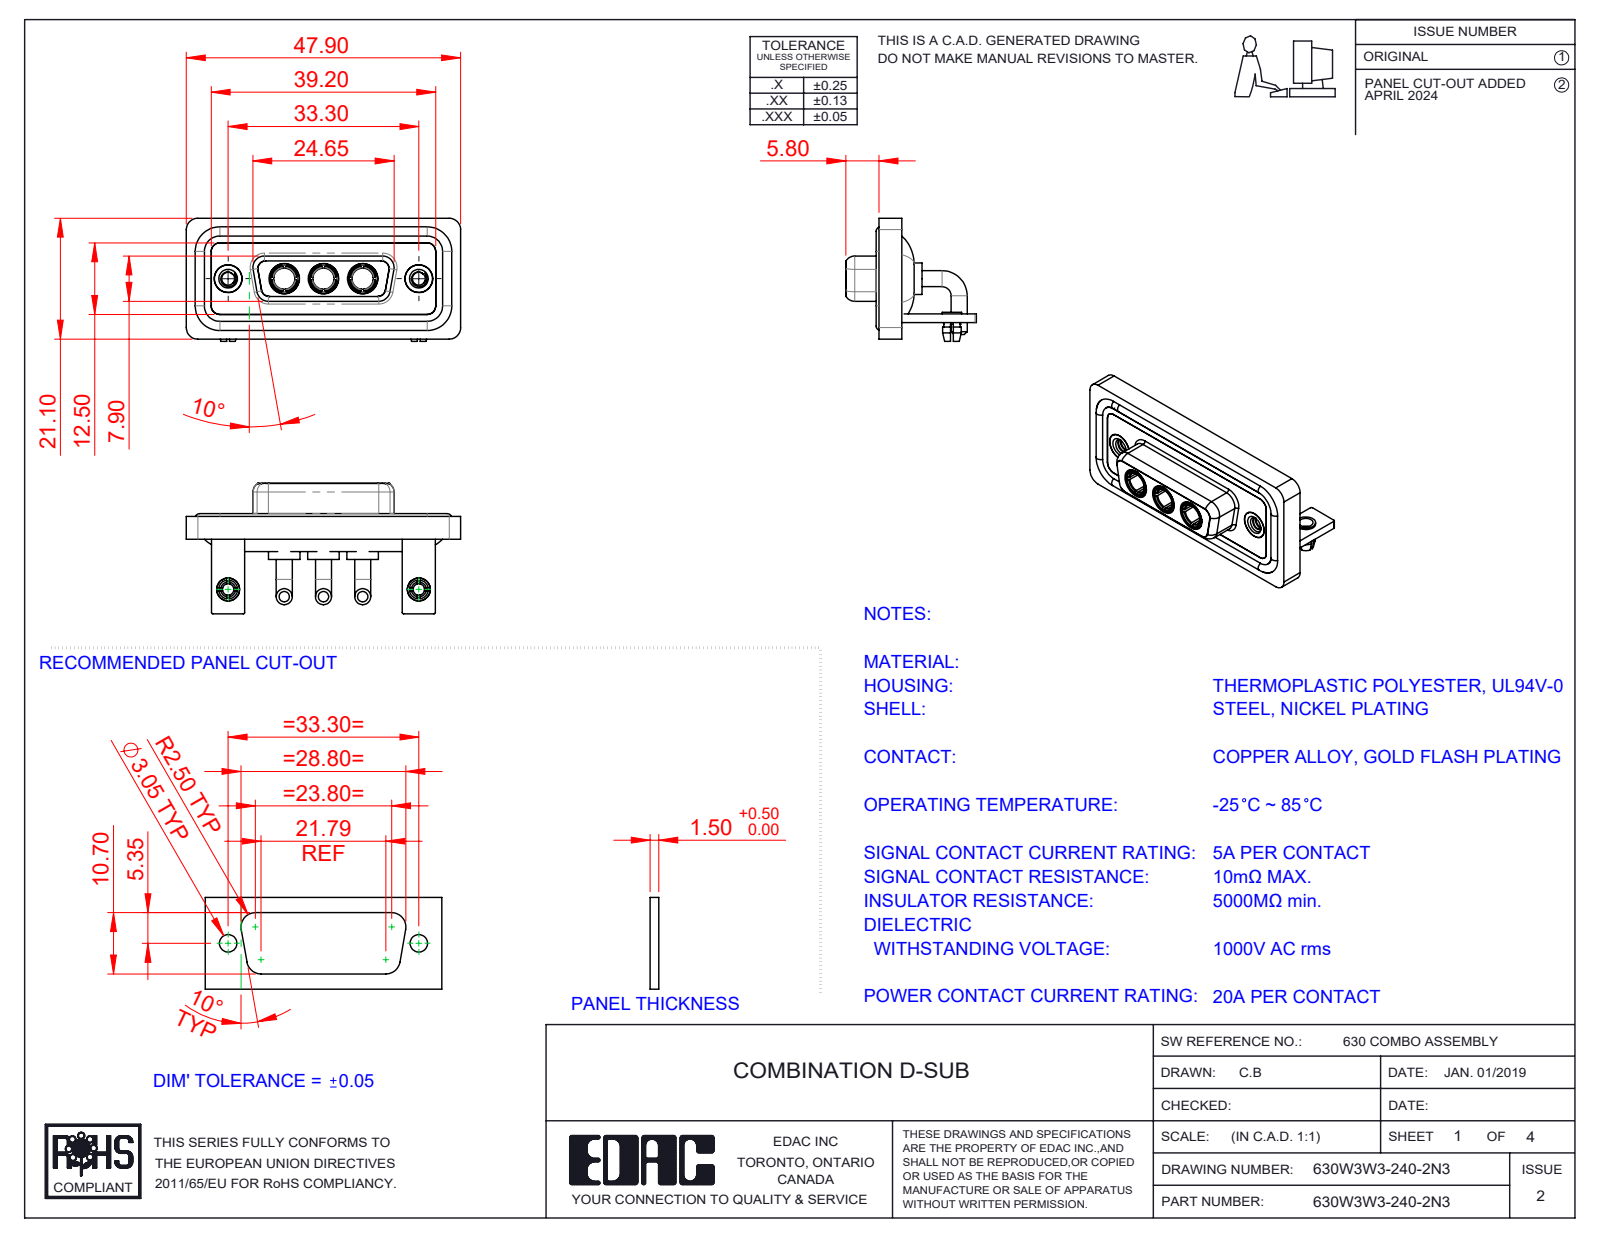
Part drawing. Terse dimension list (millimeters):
name: 630Combo Threaded Rivet_2; 630Combo Housing_3W3; Power Socket_20A RA; 630W3W3-140-2N3 (+5 more)
written by: SolidWorks 2023 (CONFIG_CONTROL_DESIGN)
unit: mm
bodies: 17 solids, 760 faces (260 planar, 319 cylindrical, 181 other)
size: 47.9 × 22.8 × 21.5
volume: 6 583 mm³; area: 10 917 mm²
holes: 5× ⌀4.85, 3× ⌀3.7, 3× ⌀5.3, 2× ⌀2, 2× ⌀2.26, 2× ⌀2.5, 2× ⌀3.2, 2× ⌀4, 2× ⌀4.05, 2× ⌀5
bosses: 6× ⌀2.8, 4× ⌀1.6, 3× ⌀5.5, 3× ⌀5.2, 3× ⌀4.96, 3× ⌀4.75, 3× ⌀3.75, 2× ⌀4.95
rounds: 21× R2, 18× R1.5, 16× R0.25, 12× R1.35, 8× R1.6, 5× R0.5, 4× R0.6, 4× R0.65
face distances: 0.4, 2.9, 1.5, 1.8, 3.7, 1.1, 4.1, 1.6, 2.5, 1.4
hole spacings: 6.85, 9.8, 16.65, 23.5, 33.3, 13.7
